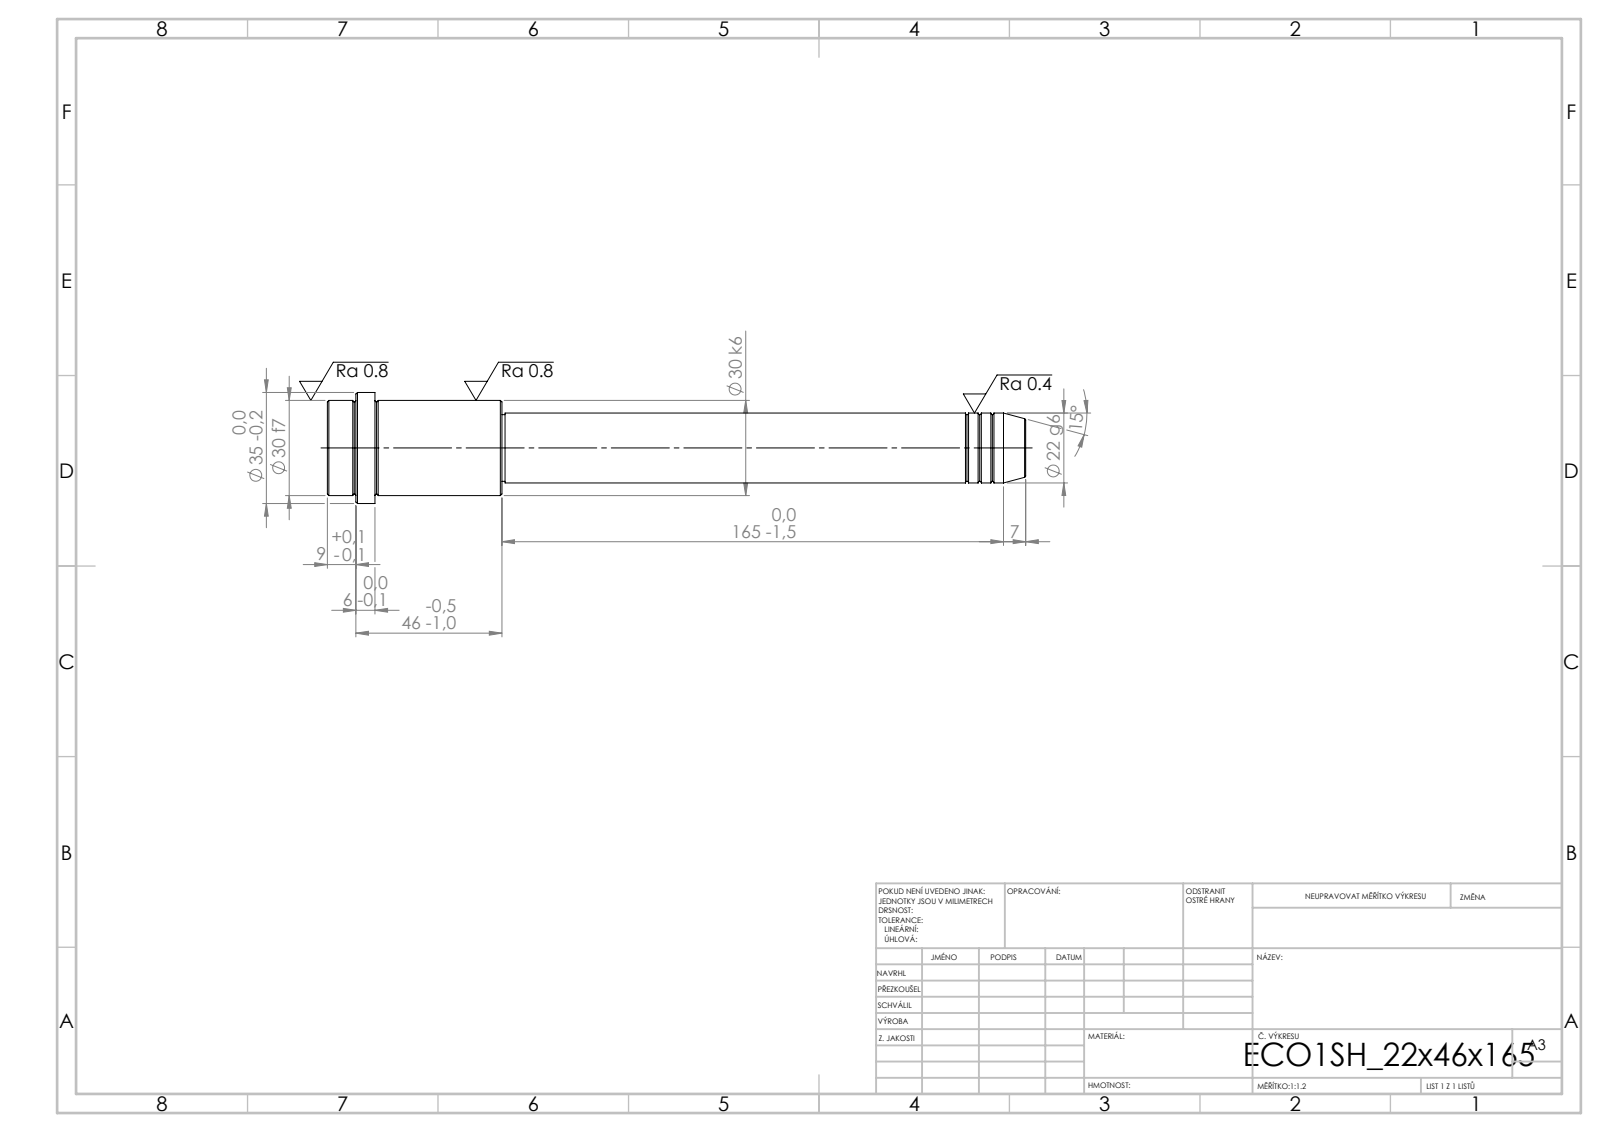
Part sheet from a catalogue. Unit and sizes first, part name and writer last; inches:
Units: inches
Overall size (bounding box): 8.661 × 1.378 × 1.378
Round bosses / shafts (diameter × count): ⌀1.378 ×1, ⌀1.181 ×1, ⌀0.866 ×1, ⌀0.827 ×1
Main face-to-face distances: 2.165, 1.575, 0.591, 6.496, 8.071, 8.661, 8.307, 1.811, 0.236, 0.354
Volume: 6.254 in³ · Surface area: 28.9 in²
Bodies: 1 solid, 52 faces (6 planar, 16 cylindrical, 30 other)
STEP written by: SolidWorks 2019 (CONFIG_CONTROL_DESIGN)
